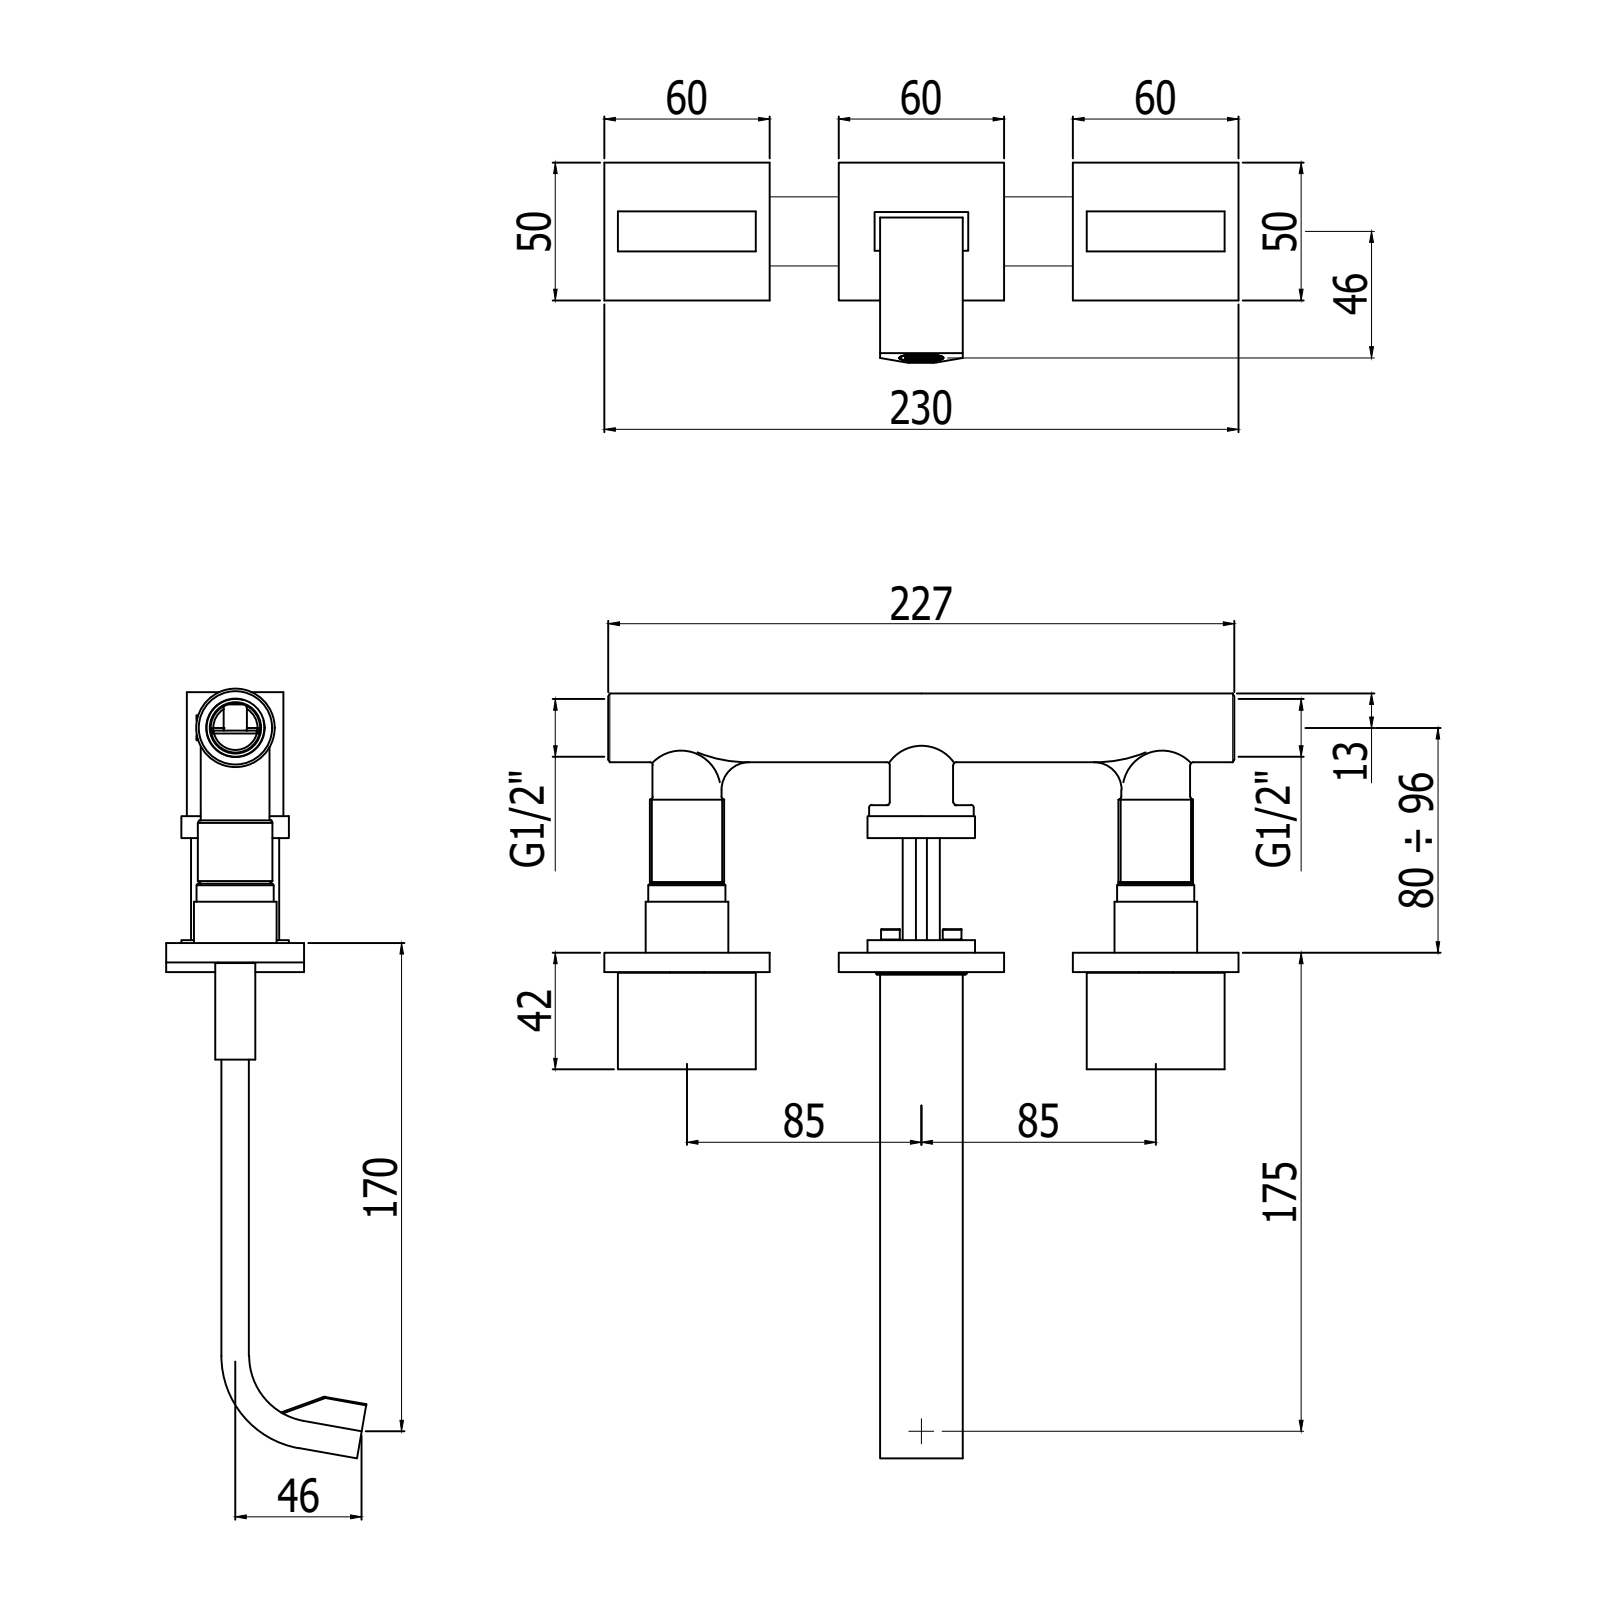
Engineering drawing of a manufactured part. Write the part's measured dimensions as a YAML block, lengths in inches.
part_name: "LEP003CR"
step_written_by: "CREO PARAMETRIC BY PTC INC, 2020044 (CONFIG_CONTROL_DESIGN)"
units: inches
bodies: {solids: 4, faces: 2424, planar: 1866, cylindrical: 385, other: 173}
overall_size: [9.055, 6.847, 2.859]
volume: 6.701
surface_area: 112
round_holes:
  - {diameter: 1.85, count: 3}
  - {diameter: 0.13, count: 2}
  - {diameter: 0.165, count: 2}
  - {diameter: 0.335, count: 2}
  - {diameter: 0.378, count: 2}
  - {diameter: 0.386, count: 2}
  - {diameter: 0.394, count: 2}
  - {diameter: 0.492, count: 2}
  - {diameter: 1.122, count: 2}
  - {diameter: 0.236, count: 1}
  - {diameter: 0.433, count: 1}
  - {diameter: 0.478, count: 1}
round_bosses_or_shafts:
  - {diameter: 0.035, count: 3}
  - {diameter: 1.181, count: 2}
  - {diameter: 0.488, count: 2}
  - {diameter: 0.15, count: 2}
  - {diameter: 0.646, count: 1}
  - {diameter: 0.597, count: 1}
  - {diameter: 0.596, count: 1}
  - {diameter: 0.591, count: 1}
partial_cylinders:
  - {radius: 0.005, count: 51}
  - {radius: 0.024, count: 5}
  - {radius: 0.059, count: 5}
  - {radius: 0.069, count: 2}
  - {radius: 0.294, count: 1}
  - {radius: 0.945, count: 1}
  - {radius: 1.004, count: 1}
  - {radius: 1.28, count: 1}
face_to_face_distances: [0.059, 0.276, 0.335, 0.148, 0.482, 0.089, 0.423, 1.181, 1.122, 0.217]
hole_center_spacings: [0.441, 2.906, 3.346, 3.787, 6.693, 0.882]
